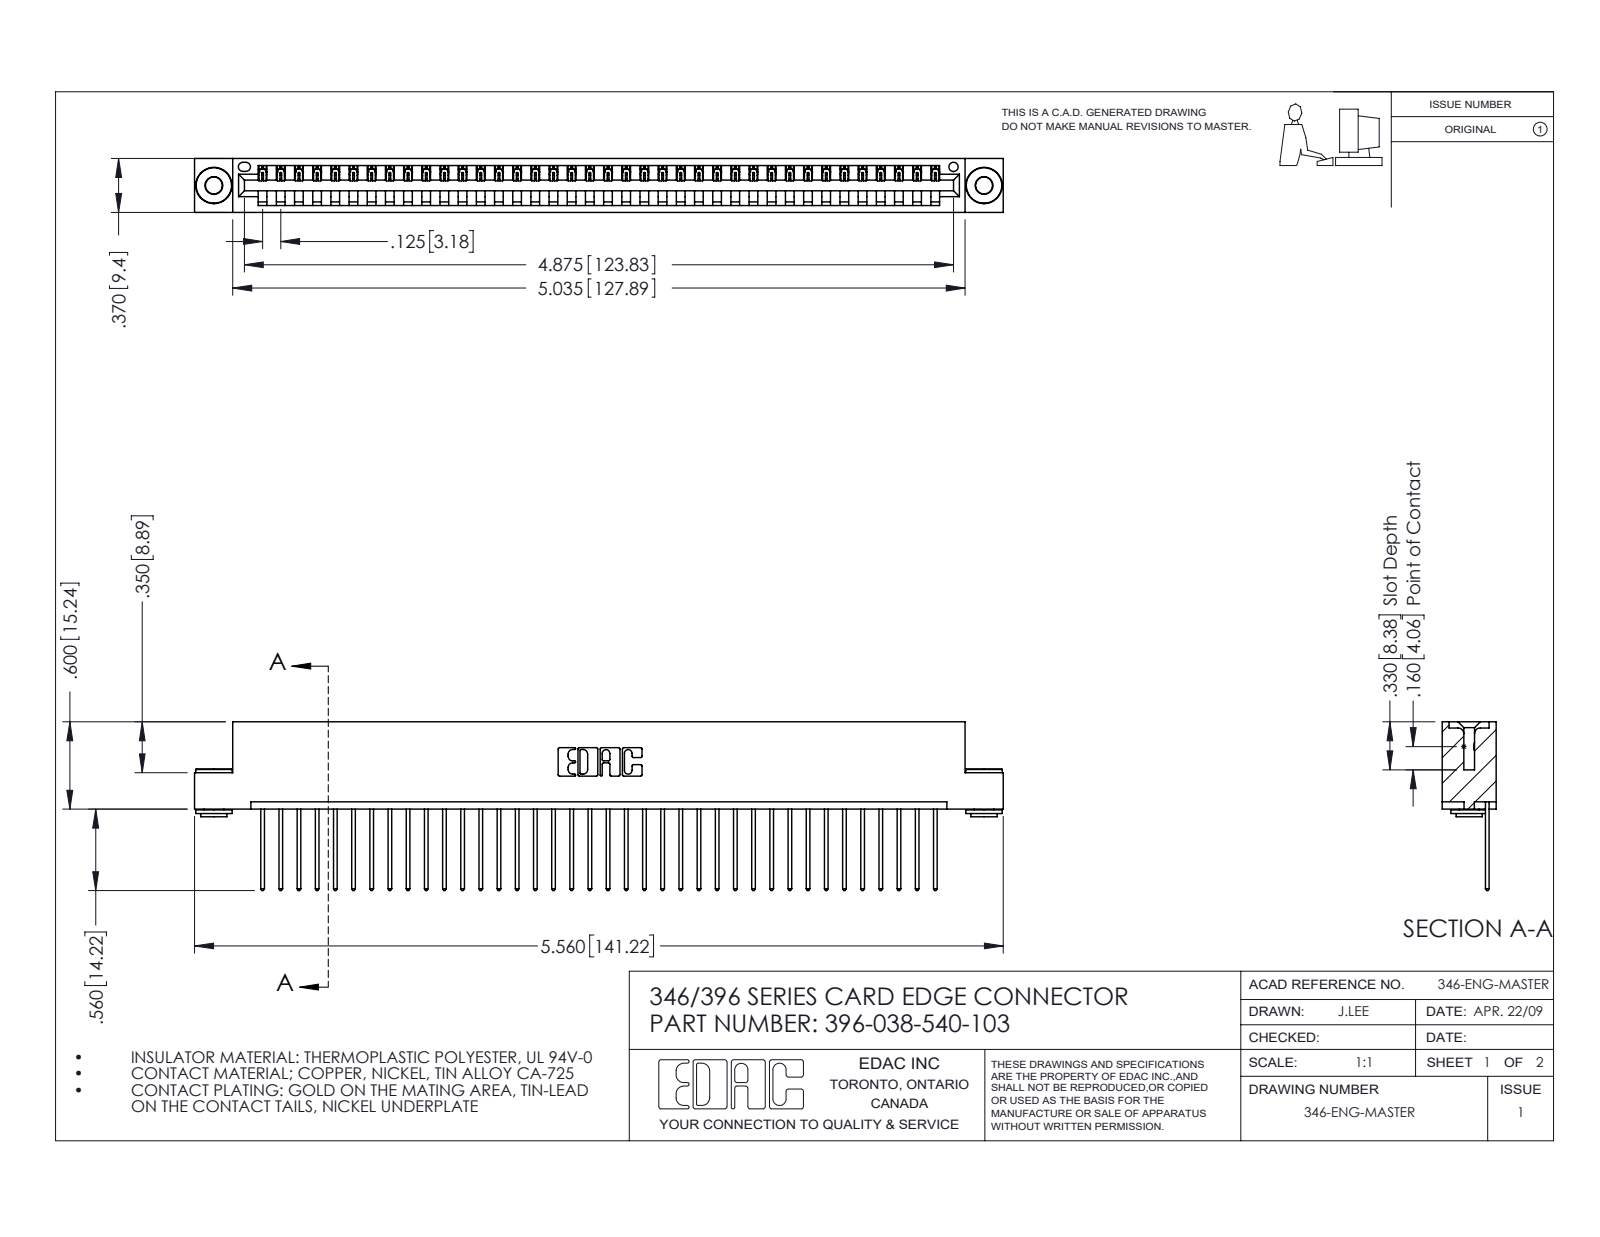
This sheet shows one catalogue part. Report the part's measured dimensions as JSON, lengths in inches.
{"part_name": "396-038-540-103; 346 Part_Flush Mounting Lugs - 0.156 Dia-TH; 345-250-002_345-250-002-102; 345-292-001_345-293-140", "step_written_by": "SolidWorks 2016 (CONFIG_CONTROL_DESIGN)", "units": "inches", "bodies": {"solids": 41, "faces": 2364, "planar": 1606, "cylindrical": 750, "other": 8}, "overall_size": [5.56, 1.16, 0.37], "volume_in3": 0.828, "surface_area_in2": 27.13, "round_holes": [[0.116, 2], [0.156, 2], [0.064, 1]], "round_bosses_or_shafts": [[0.25, 2], [0.18, 2], [0.136, 2]], "partial_cylinders_radius": [[0.006, 76], [0.01, 76], [0.01, 22], [0.007, 6], [0.031, 6], [0.026, 3], [0.031, 2], [0.04, 2]], "face_to_face_distances": [0.048, 0.322, 0.37, 0.25, 0.025, 0.072, 0.298, 0.148, 0.222, 0.1], "hole_center_spacings": [0.246, 5.086, 5.295]}
